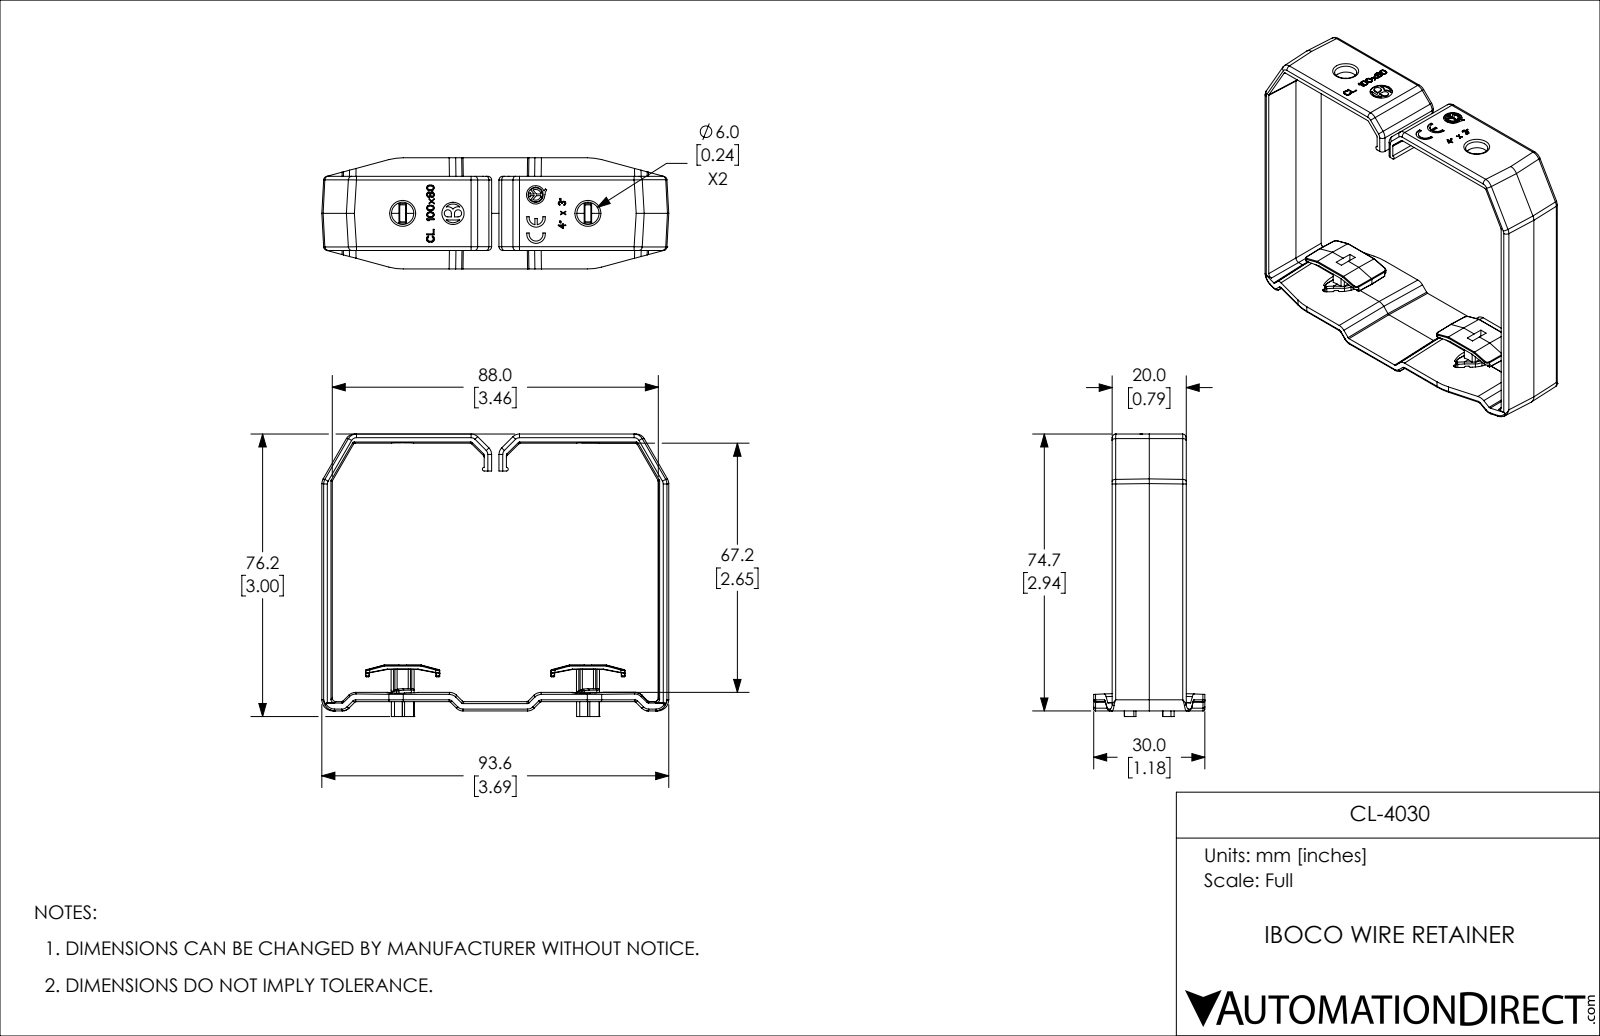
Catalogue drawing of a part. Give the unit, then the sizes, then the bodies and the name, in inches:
Units: inches
Overall size (bounding box): 3.685 × 3 × 1.181
Round holes (diameter × count): ⌀0.236 ×3, ⌀0.197 ×1
Round bosses / shafts (diameter × count): ⌀0.161 ×1
Partial cylindrical surfaces — rounded edges, fillets, slot ends (radius × count): R0.02 ×66, R0.008 ×36, R0.039 ×34, R0.098 ×30, R0.012 ×12, R0.016 ×12, R0.026 ×4, R0.047 ×4
Main face-to-face distances: 2.643, 0.098, 3.461, 3.681, 2.843, 2.941, 2.741, 1.392, 0.787, 0.079
Hole centre spacings: 0.535, 0.589, 0.9, 1.427, 1.434, 1.969
Volume: 1.039 in³ · Surface area: 27.27 in²
Bodies: 1 solid, 1021 faces (665 planar, 279 cylindrical, 77 other)
Part name (STEP PRODUCT): CL-4030
STEP written by: SolidWorks 2019 (CONFIG_CONTROL_DESIGN)
